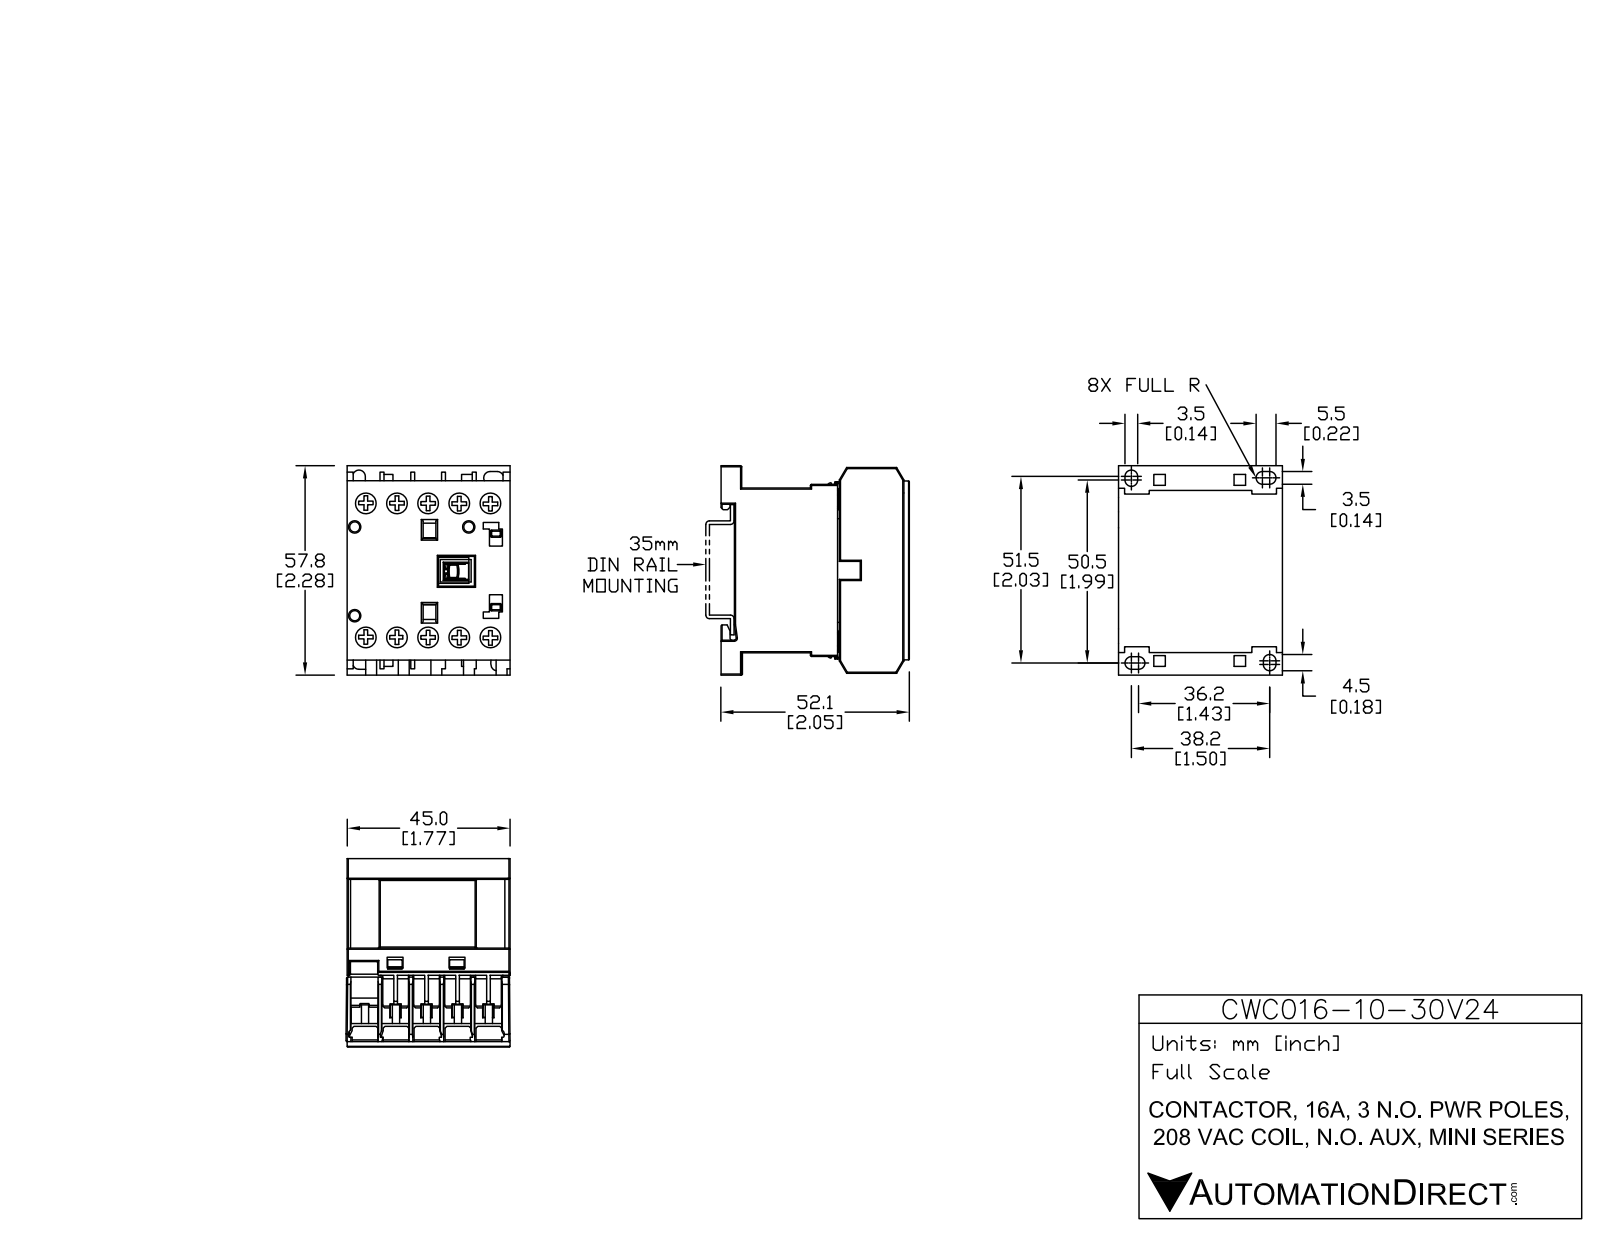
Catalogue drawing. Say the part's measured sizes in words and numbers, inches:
The part is named "CWC16-10-30V24". Its 3-D file was written by "SolidWorks 2013 (AUTOMOTIVE_DESIGN)". It is 15 solids with 535 faces: 445 planar, 90 cylindrical and 0 other. Overall it measures 2.285 by 2.052 by 1.801 inches. Its volume is 5.927 cubic inches and its surface area 47.18 square inches. Round holes: 10 of diameter 0.244, 3 of diameter 0.11. Round bosses or shafts: 10 of diameter 0.232. Partial cylindrical surfaces (rounded edges, fillets, slot ends): 20 of radius 0.012, 6 of radius 0.068, 2 of radius 0.068, 1 of radius 0.013, 1 of radius 0.017, 1 of radius 0.022. The main face-to-face distances are 0.325, 1.791, 0.049, 0.65, 0.374, 0.217, 0.699, 0.202, 0.419, 0.276. The hole center spacings are 0.337, 1.494, 0.673, 1.603, 1.455, 1.01, 1.771, 0.272.
